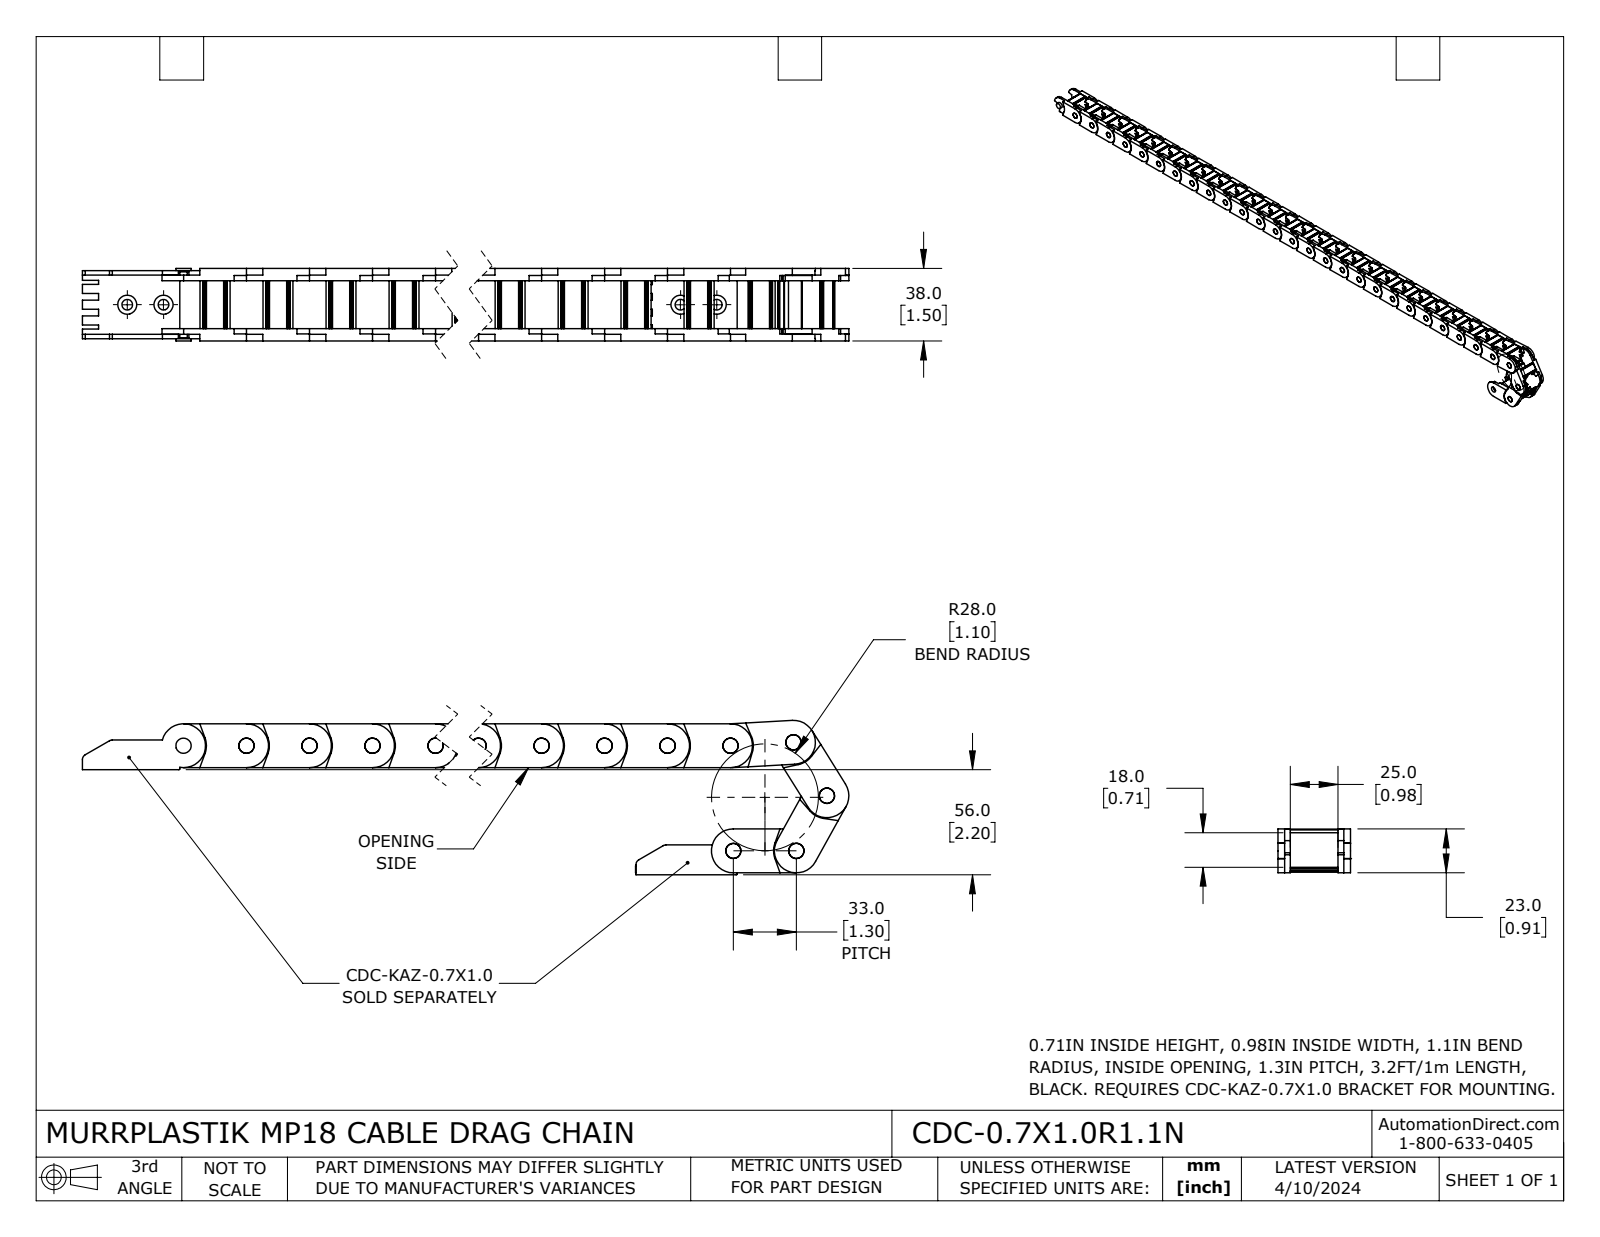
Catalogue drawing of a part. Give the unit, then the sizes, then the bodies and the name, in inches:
Units: inches
Overall size (bounding box): 36.665 × 3.143 × 1.496
Round holes (diameter × count): ⌀0.315 ×30
Round bosses / shafts (diameter × count): ⌀0.315 ×1
Partial cylindrical surfaces — rounded edges, fillets, slot ends (radius × count): R0.02 ×120, R0.059 ×120, R0.008 ×60, R0.012 ×60, R0.453 ×31, R0.47 ×31, R0.197 ×30, R0.215 ×30
Main face-to-face distances: 0.256, 1.24, 1.496, 0.138, 1.358, 0.118, 1.102, 0.984, 0.146, 1.35
Hole centre spacings: 1.299, 2.598, 3.898, 5.197, 6.496, 7.795, 9.094, 10.394
Volume: 18.75 in³ · Surface area: 347 in²
Bodies: 30 solids, 2550 faces (1290 planar, 1260 cylindrical, 0 other)
Part name (STEP PRODUCT): CDC-0.7X1.0R1.1N
STEP written by: SolidWorks 2023 (CONFIG_CONTROL_DESIGN)
